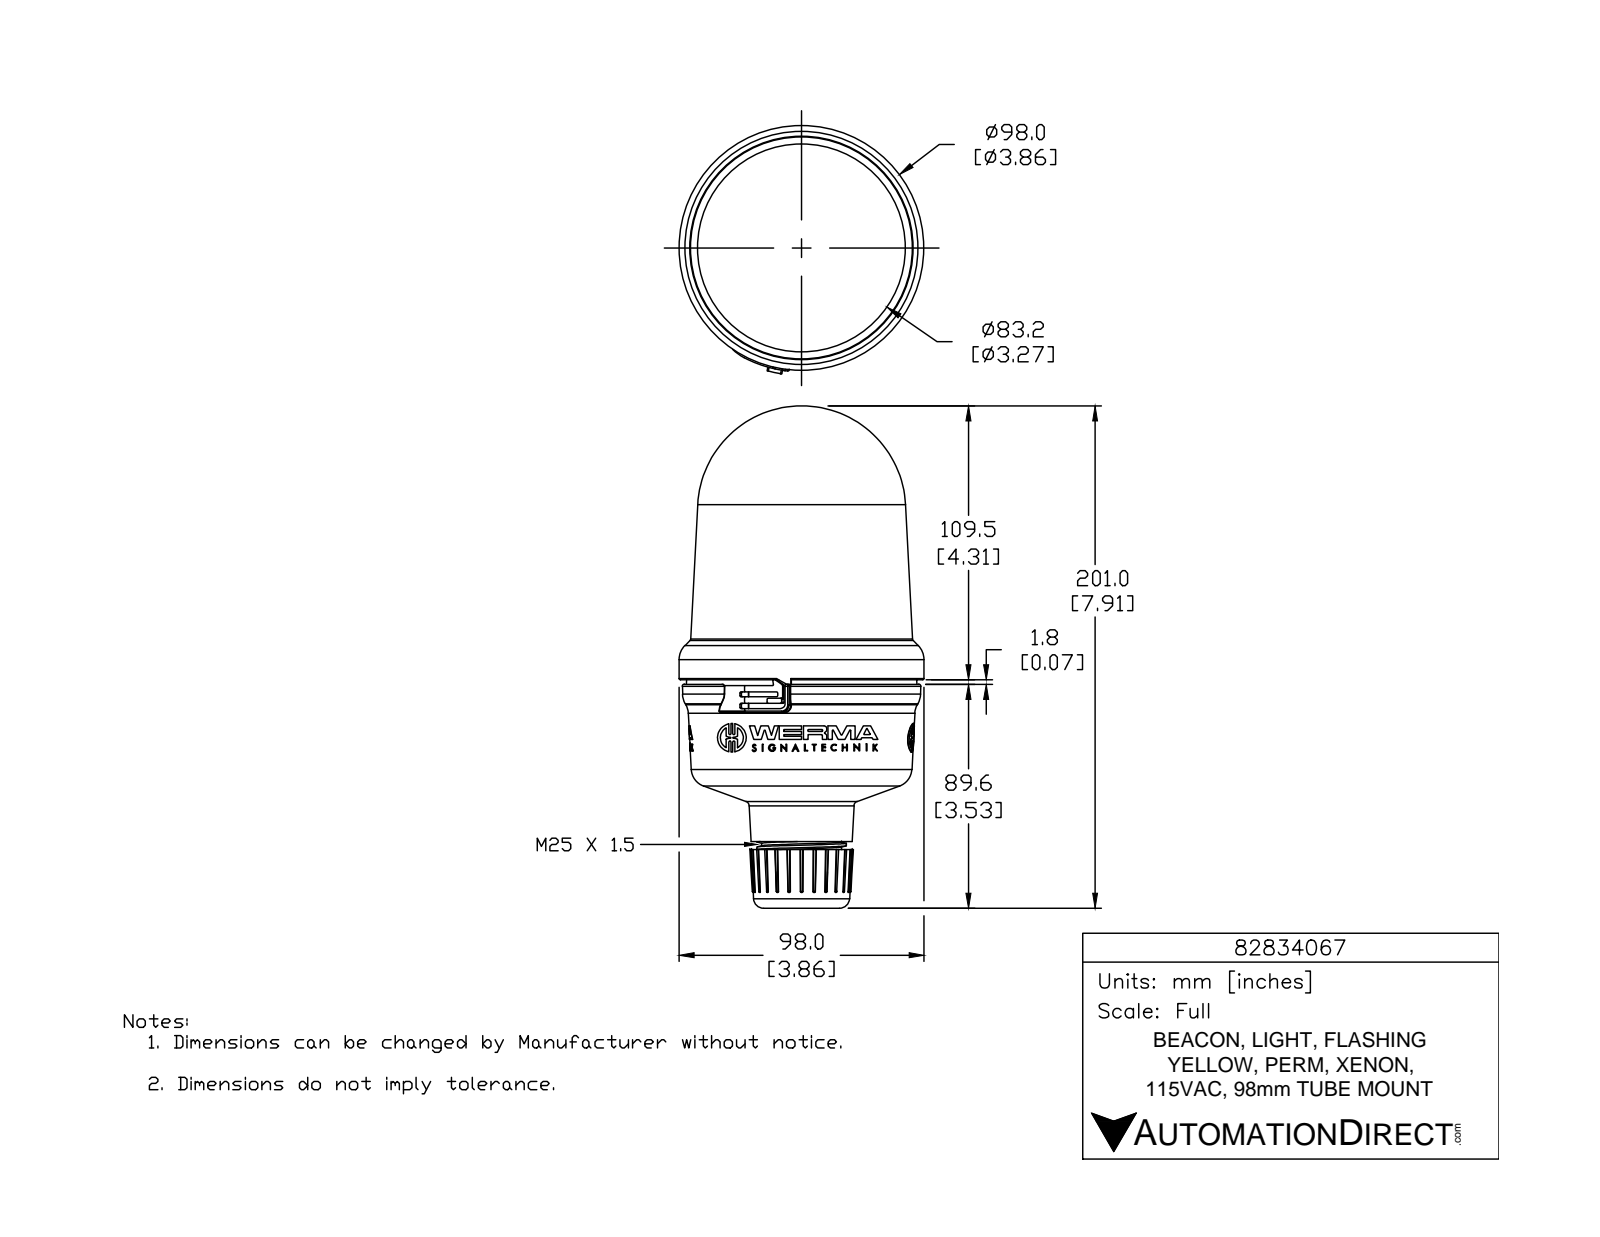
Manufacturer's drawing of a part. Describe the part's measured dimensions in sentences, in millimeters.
The part is named "82834067". Its 3-D file was written by "SolidWorks 2015 (AUTOMOTIVE_DESIGN)". It is 1 solid with 1006 faces: 554 planar, 189 cylindrical and 263 other. Overall it measures 201 by 99.4 by 98 millimeters. Its volume is 896 400 cubic millimeters and its surface area 58 960 square millimeters. Round holes: 3 of diameter 2, 1 of diameter 25.7, 1 of diameter 26. Round bosses or shafts: 3 of diameter 11.5, 3 of diameter 2.9, 1 of diameter 98, 1 of diameter 35.8, 1 of diameter 32. Partial cylindrical surfaces (rounded edges, fillets, slot ends): 12 of radius 0.5, 9 of radius 0.2, 6 of radius 0.2, 6 of radius 0.4, 6 of radius 0.4, 6 of radius 0.4, 6 of radius 6.7, 3 of radius 0.2. The main face-to-face distances are 56.2, 11.7, 68, 8.5, 3.2, 64.7, 66.1, 62.9, 54.4, 1.9.
